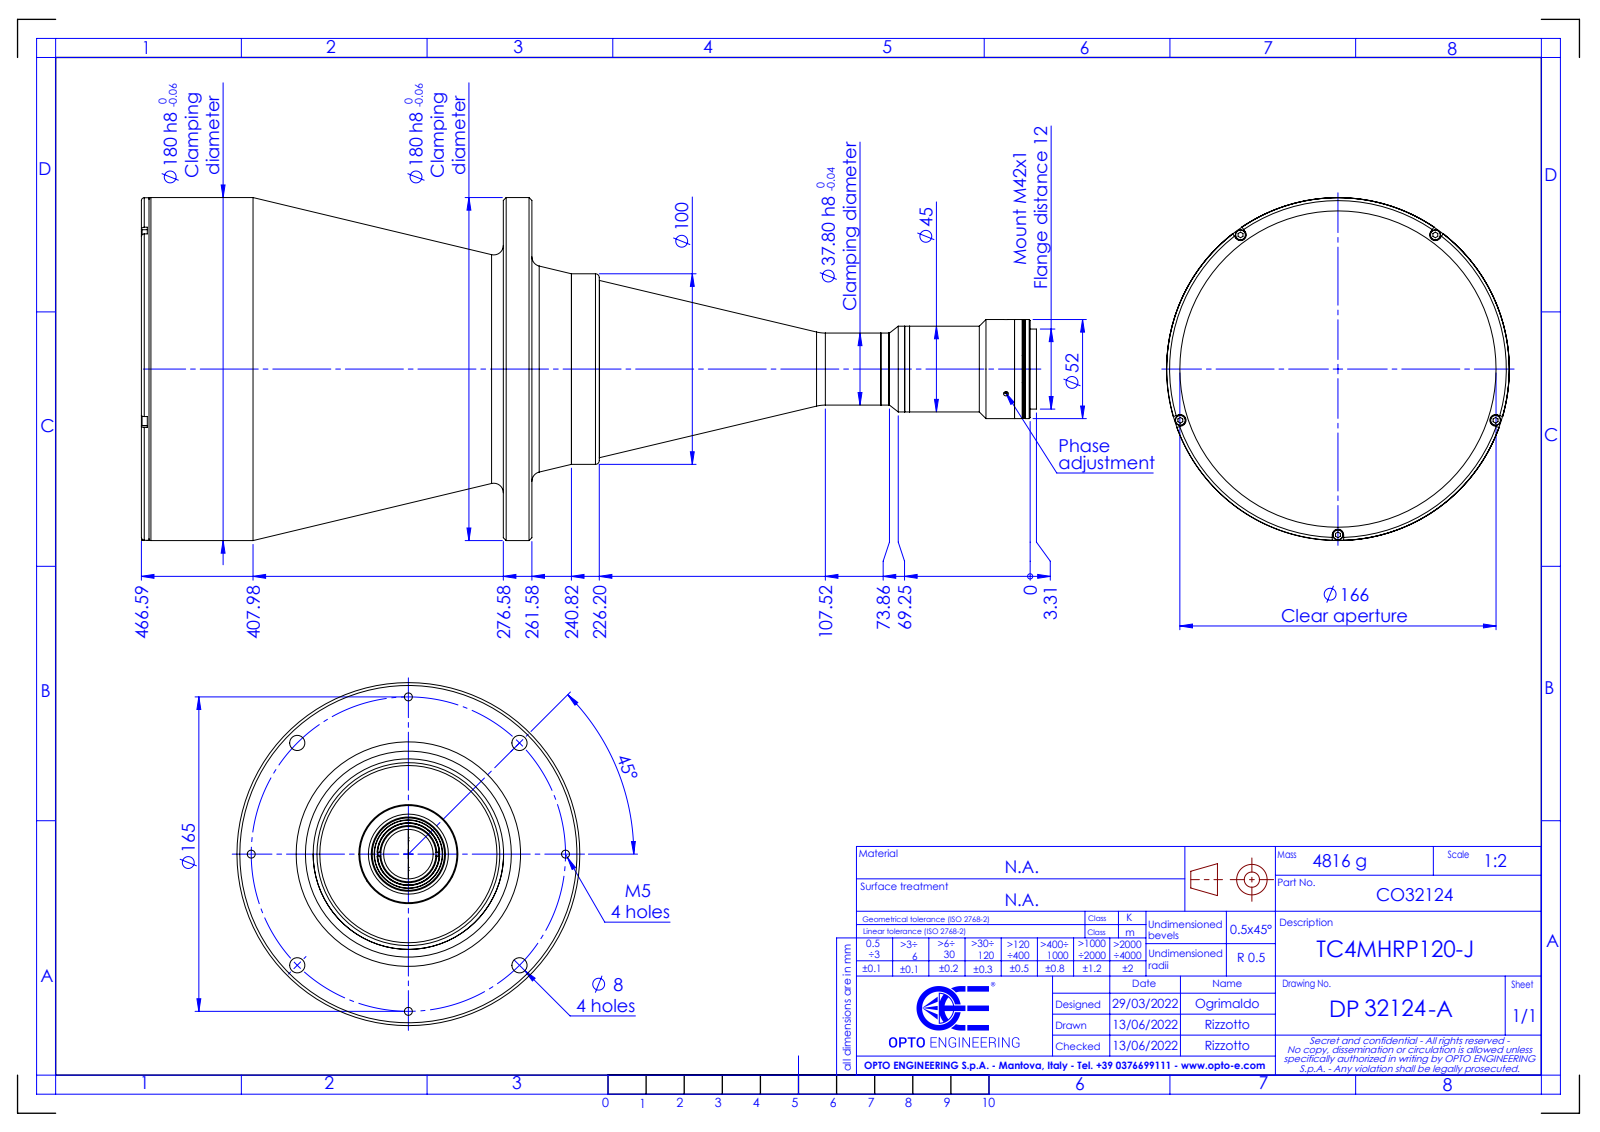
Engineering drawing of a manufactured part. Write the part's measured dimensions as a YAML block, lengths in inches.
part_name: "DP32124-A_TC4MHRP120-J"
step_written_by: "SolidWorks 2021 (CONFIG_CONTROL_DESIGN)"
units: inches
bodies: {solids: 0, faces: 201, planar: 58, cylindrical: 86, other: 57}
overall_size: [18.5, 7.087, 7.087]
round_holes:
  - {diameter: 0.165, count: 4}
  - {diameter: 0.315, count: 4}
  - {diameter: 0.098, count: 3}
  - {diameter: 1.496, count: 1}
  - {diameter: 1.614, count: 1}
  - {diameter: 6.535, count: 1}
  - {diameter: 6.724, count: 1}
round_bosses_or_shafts:
  - {diameter: 0.217, count: 5}
  - {diameter: 7.087, count: 1}
  - {diameter: 7.079, count: 1}
  - {diameter: 3.937, count: 1}
  - {diameter: 3.661, count: 1}
  - {diameter: 2.047, count: 1}
  - {diameter: 2.039, count: 1}
  - {diameter: 1.772, count: 1}
partial_cylinders:
  - {radius: 0.118, count: 4}
face_to_face_distances: [0.591, 7.481, 8.071, 0.157, 7.323, 7.914, 18.269, 18.111, 10.788, 10.198]
hole_center_spacings: [2.486, 6.002, 3.248, 3.248, 4.593, 4.594, 6.496, 6.496]
